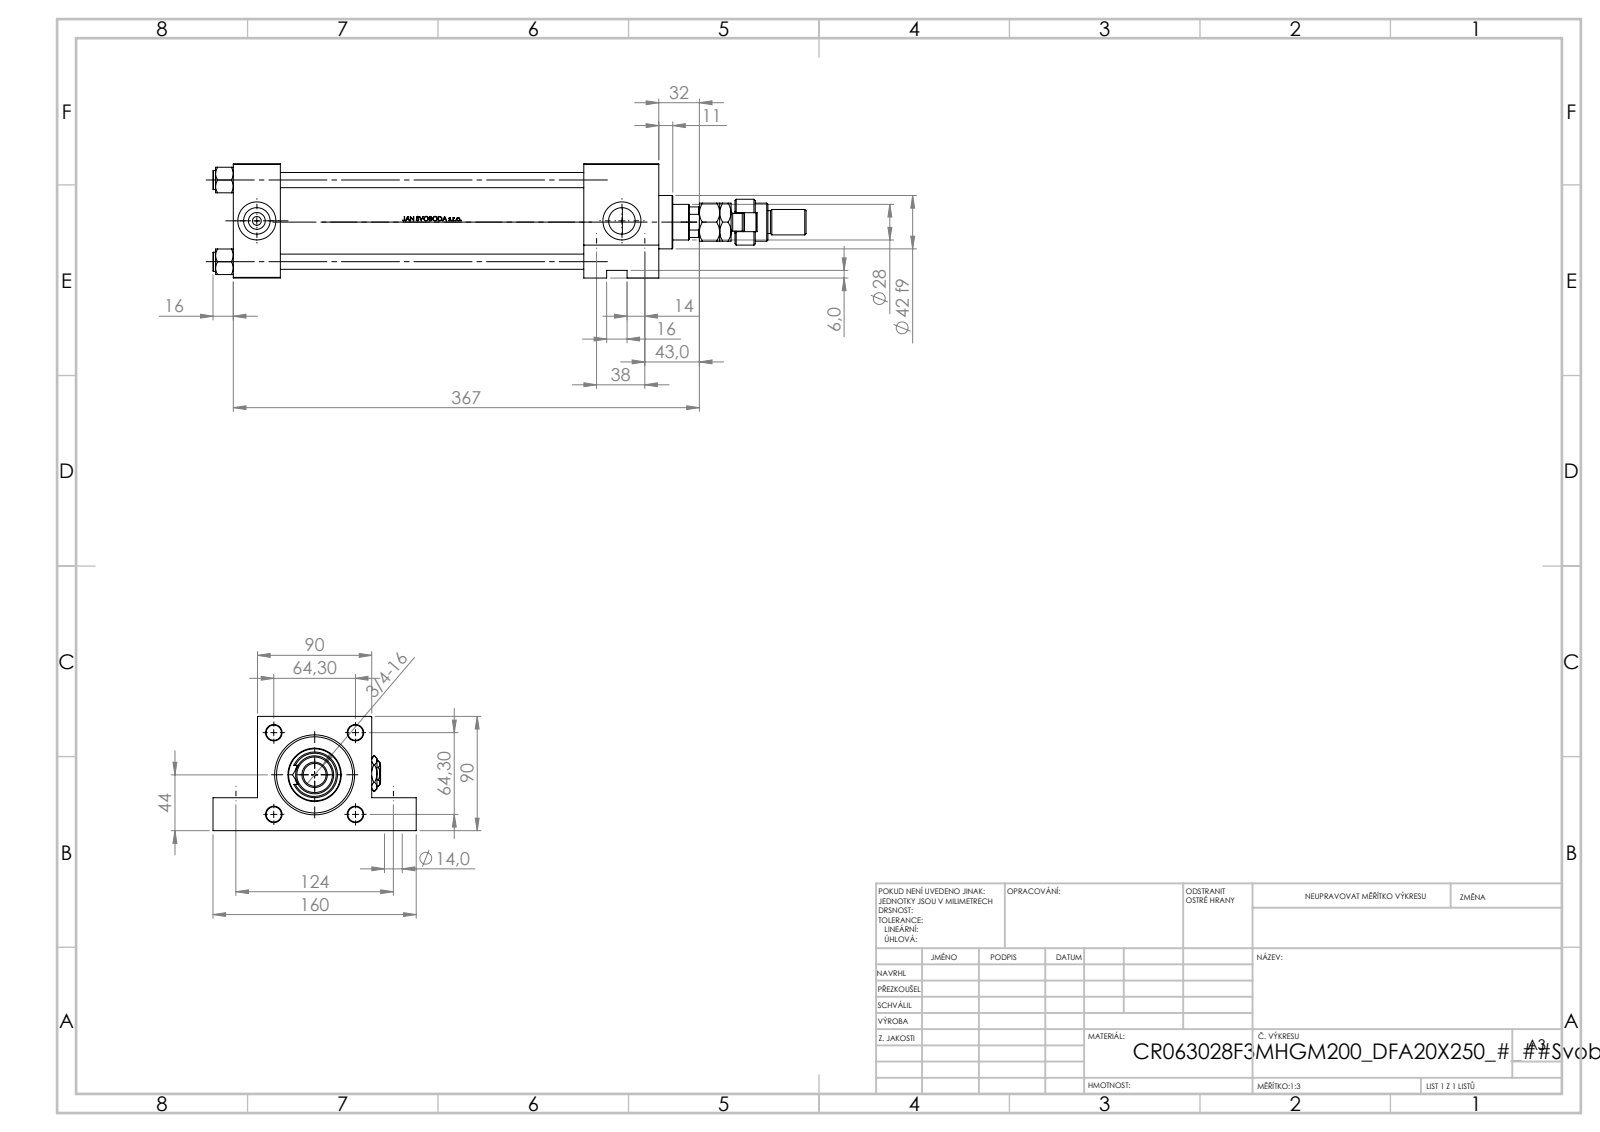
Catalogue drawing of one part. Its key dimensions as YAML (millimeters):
part_name: "V215CR_F_TYCINKA; MFA; V215CR_F_Body; NUT_M5_F (+4 more)"
step_written_by: "SolidWorks 2019 (CONFIG_CONTROL_DESIGN)"
units: millimeters
bodies: {solids: 15, faces: 1285, planar: 512, cylindrical: 147, other: 626}
overall_size: [467, 160, 90]
volume: 1376000
surface_area: 329522
round_holes:
  - {diameter: 12, count: 4}
  - {diameter: 14, count: 4}
  - {diameter: 20.96, count: 3}
  - {diameter: 30, count: 3}
  - {diameter: 7, count: 2}
  - {diameter: 18.5, count: 1}
  - {diameter: 20, count: 1}
  - {diameter: 28, count: 1}
  - {diameter: 31, count: 1}
  - {diameter: 50, count: 1}
  - {diameter: 60, count: 1}
  - {diameter: 63, count: 1}
round_bosses_or_shafts:
  - {diameter: 15, count: 4}
  - {diameter: 69, count: 1}
  - {diameter: 42, count: 1}
  - {diameter: 36, count: 1}
  - {diameter: 30, count: 1}
  - {diameter: 22, count: 1}
  - {diameter: 20, count: 1}
  - {diameter: 18, count: 1}
partial_cylinders:
  - {radius: 7.5, count: 1}
  - {radius: 12, count: 1}
  - {radius: 13.5, count: 1}
face_to_face_distances: [90, 37, 335, 298, 59, 276, 239, 26, 64, 35]
hole_center_spacings: [64.3, 38, 44.77, 46.18, 90.93, 124, 129.69, 10]
